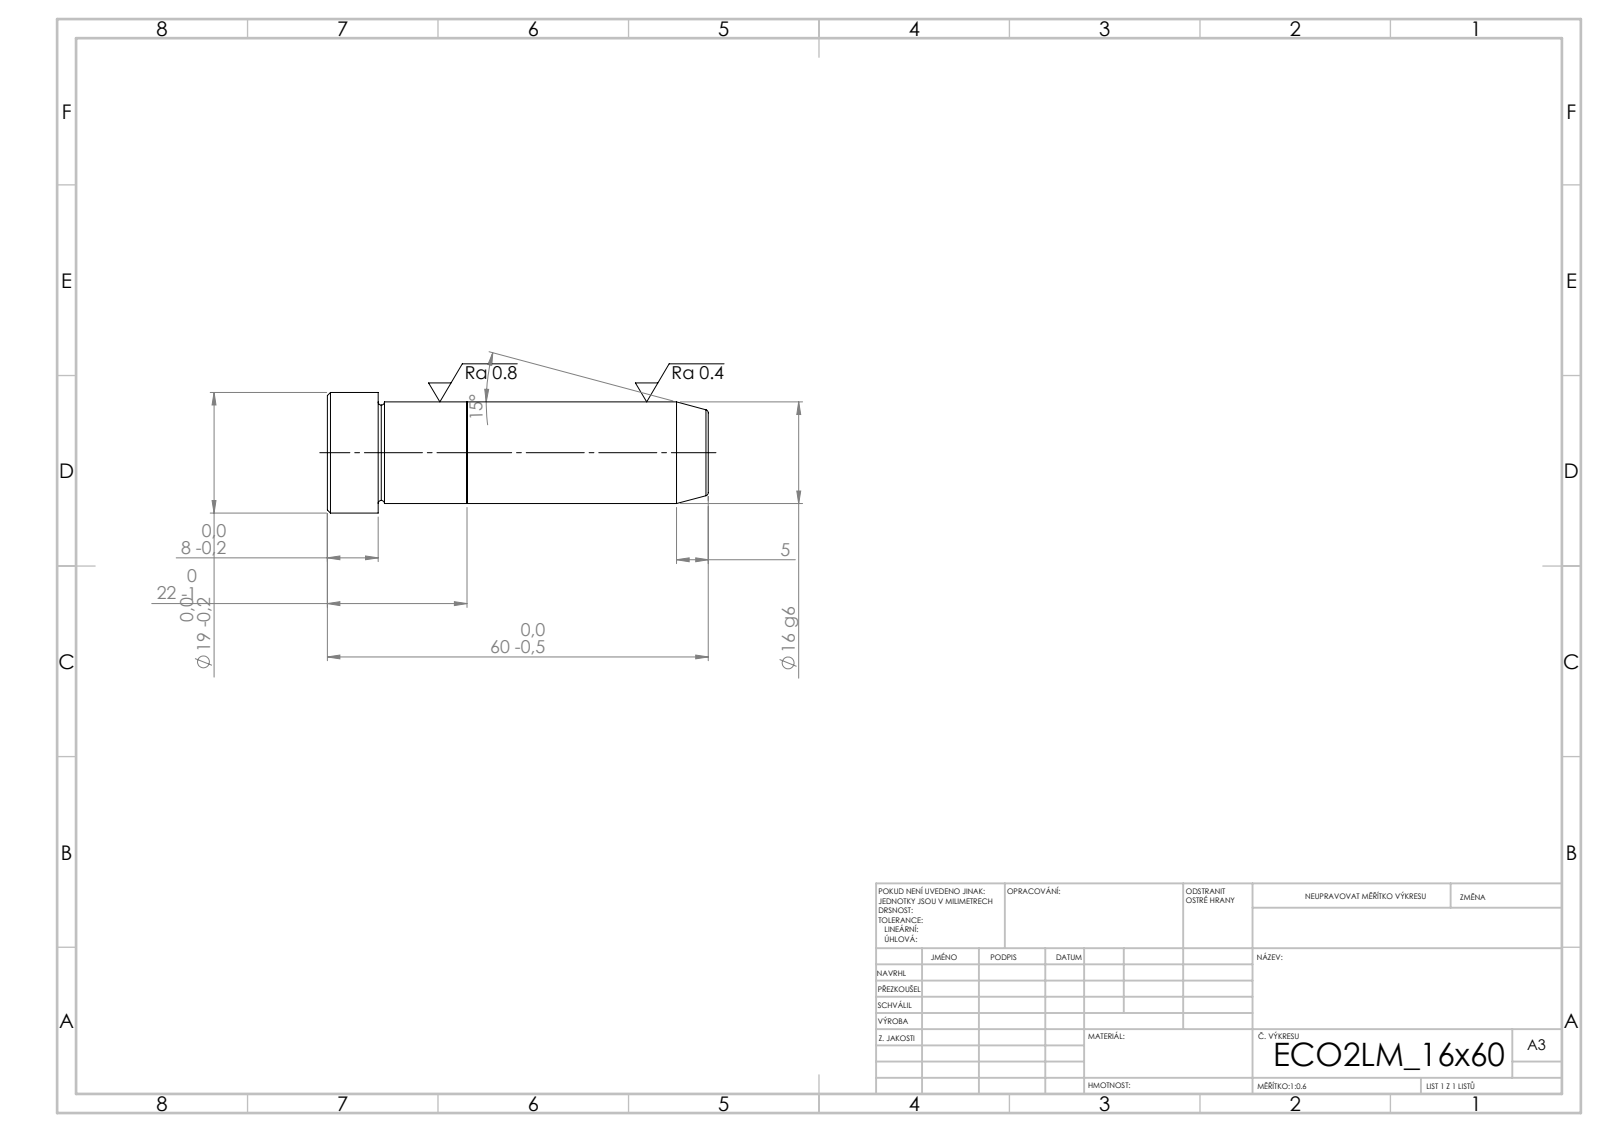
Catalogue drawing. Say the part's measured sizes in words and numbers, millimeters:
Its 3-D file was written by "SolidWorks 2019 (CONFIG_CONTROL_DESIGN)". It is 2 solids with 21 faces: 5 planar, 6 cylindrical and 10 other. Overall it measures 60 by 19 by 19 millimeters. Its volume is 12 537 cubic millimeters and its surface area 3 989 square millimeters. Round bosses or shafts: 1 of diameter 19, 1 of diameter 16. The main face-to-face distances are 22, 38, 60, 52, 14, 8.
